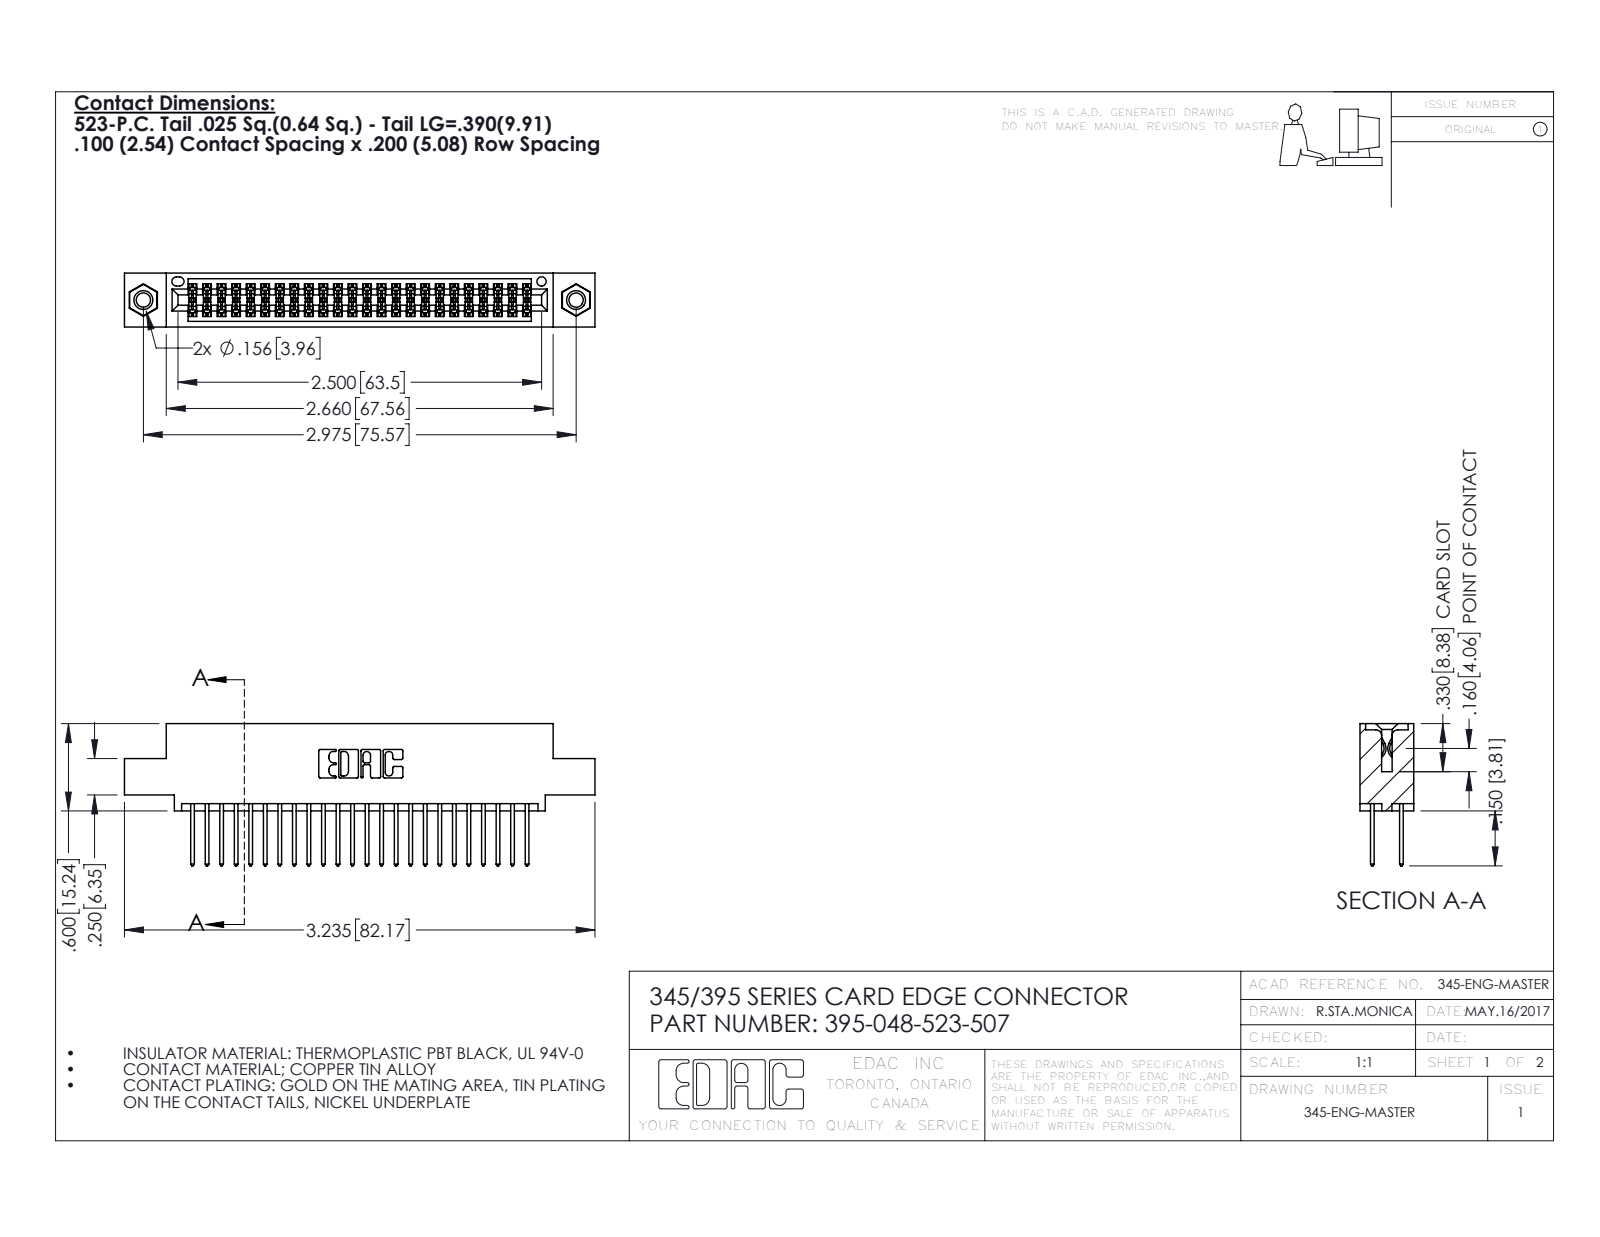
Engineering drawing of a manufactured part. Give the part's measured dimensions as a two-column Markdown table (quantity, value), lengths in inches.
| quantity | value |
| --- | --- |
| part name | 345 Part_0.110 Offset - 0.156 Dia-TI; 395-048-523-507; 345-292-001_345-293-123; 345-250-001_345-250-005-103 |
| STEP written by | SolidWorks 2016 (CONFIG_CONTROL_DESIGN) |
| units | inches |
| bodies | 51 solids, 2590 faces (1700 planar, 874 cylindrical, 16 other) |
| overall size | 3.235 × 0.977 × 0.37 |
| volume | 0.478 in³ |
| surface area | 18.26 in² |
| round holes (diameter × count) | 0.098 × 2, 0.125 × 2, 0.156 × 2, 0.064 × 1 |
| round bosses / shafts (diameter × count) | 0.155 × 2 |
| partial cylindrical surfaces (radius × count) | 0.006 × 72, 0.01 × 48, 0.01 × 22, 0.007 × 6, 0.031 × 6, 0.026 × 3, 0.014 × 2, 0.019 × 2 |
| main face-to-face distances | 0.072, 0.298, 0.2, 0.098, 0.272, 0.025, 0.37, 0.225, 0.175, 0.149 |
| hole center spacings | 0.27, 2.741, 2.975 |
